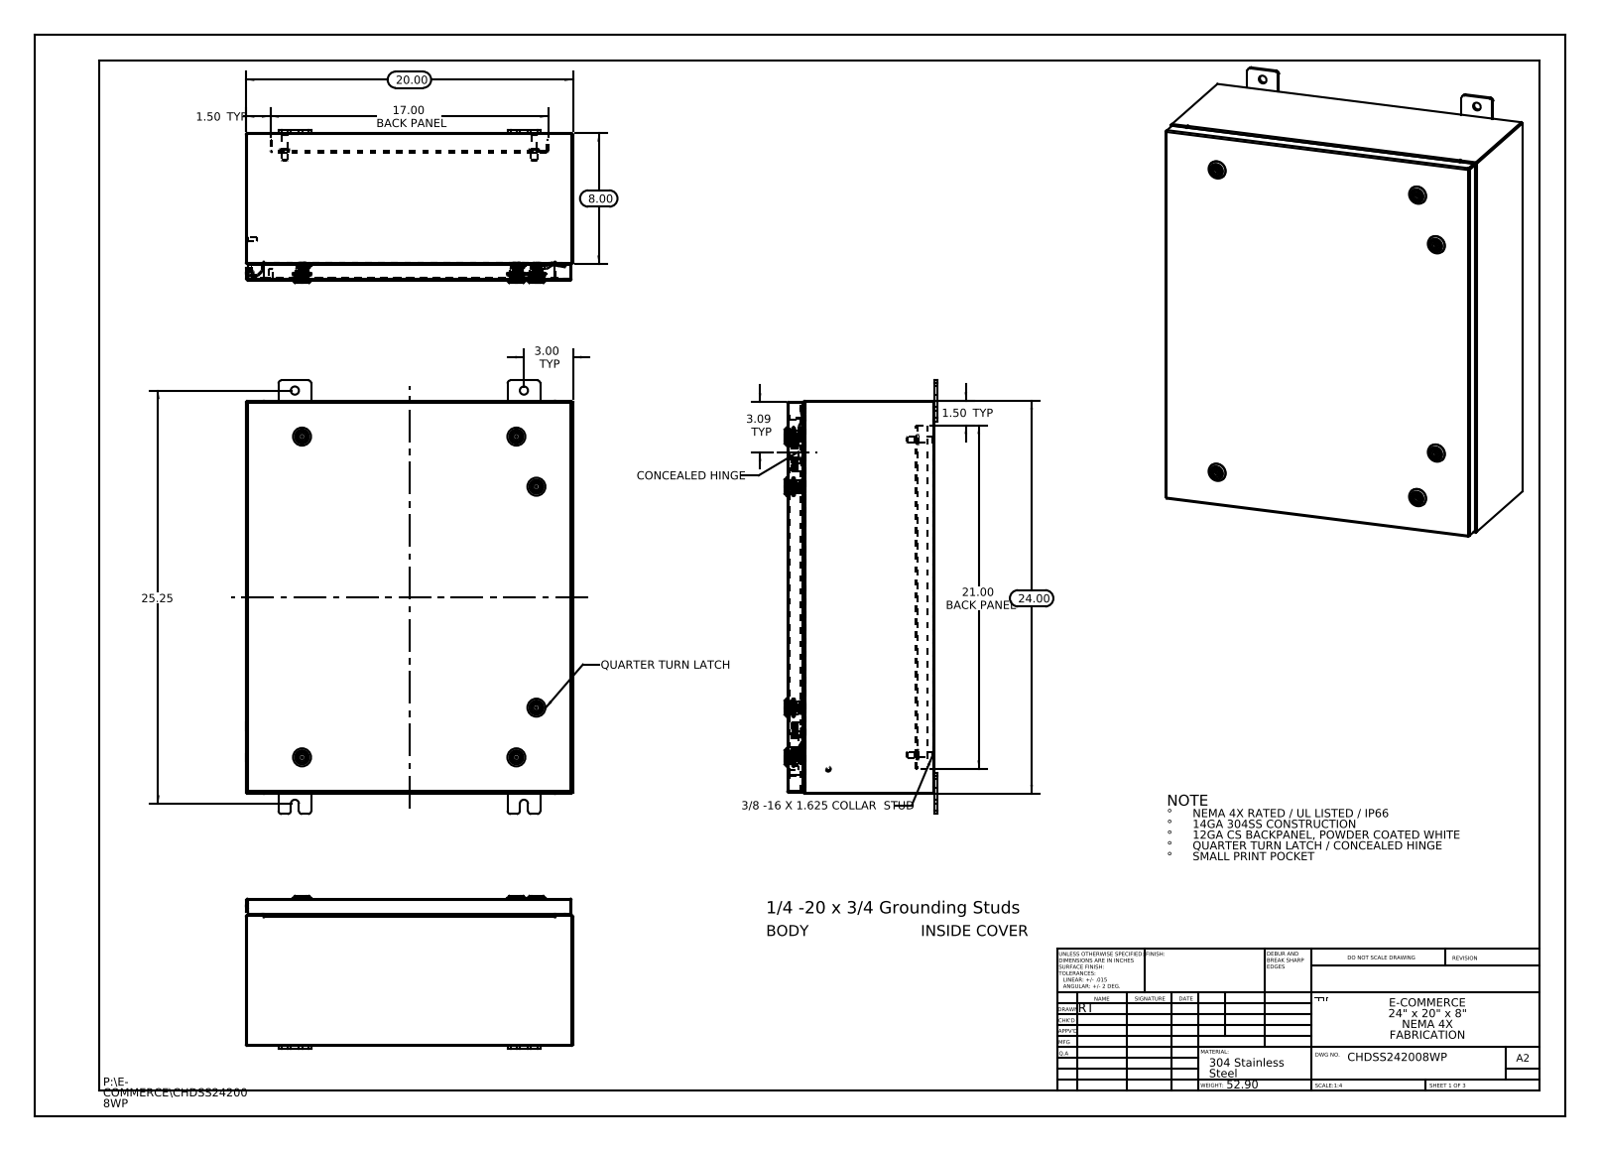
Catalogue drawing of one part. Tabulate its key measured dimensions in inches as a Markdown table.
| quantity | value |
| --- | --- |
| part name | CHDSS242008WP; CHDSS242008WP Backpanel; CHDSS242008WP Bottom; Housing-211301-IB-Industrilas_Housing-211301-IB-Industrilas (+8 more) |
| STEP written by | SolidWorks 2013 (CONFIG_CONTROL_DESIGN) |
| units | inches |
| bodies | 55 solids, 5420 faces (1592 planar, 1692 cylindrical, 2136 other) |
| overall size | 26.5 × 20 × 9.356 |
| volume | 189.1 in³ |
| surface area | 4 727 in² |
| round holes (diameter × count) | 0.5 × 8, 0.197 × 6, 0.394 × 6, 0.4 × 6, 0.63 × 6, 0.787 × 6, 0.136 × 4, 0.211 × 2 |
| round bosses / shafts (diameter × count) | 0.236 × 8, 1.102 × 6, 0.78 × 6, 0.626 × 6, 0.61 × 6, 0.531 × 6, 0.392 × 6, 0.114 × 6 |
| partial cylindrical surfaces (radius × count) | 0.006 × 198, 0.118 × 198, 0.028 × 72, 0.02 × 24, 0.19 × 24, 0.197 × 24, 0.013 × 20, 0.088 × 18 |
| main face-to-face distances | 0.075, 0.074, 9.01, 8.935, 8.936, 8.861, 0.104, 19.925, 1, 1.075 |
| hole center spacings | 1.858, 2.878, 3.065, 13.1, 14, 15.25, 15.655, 16.376 |
